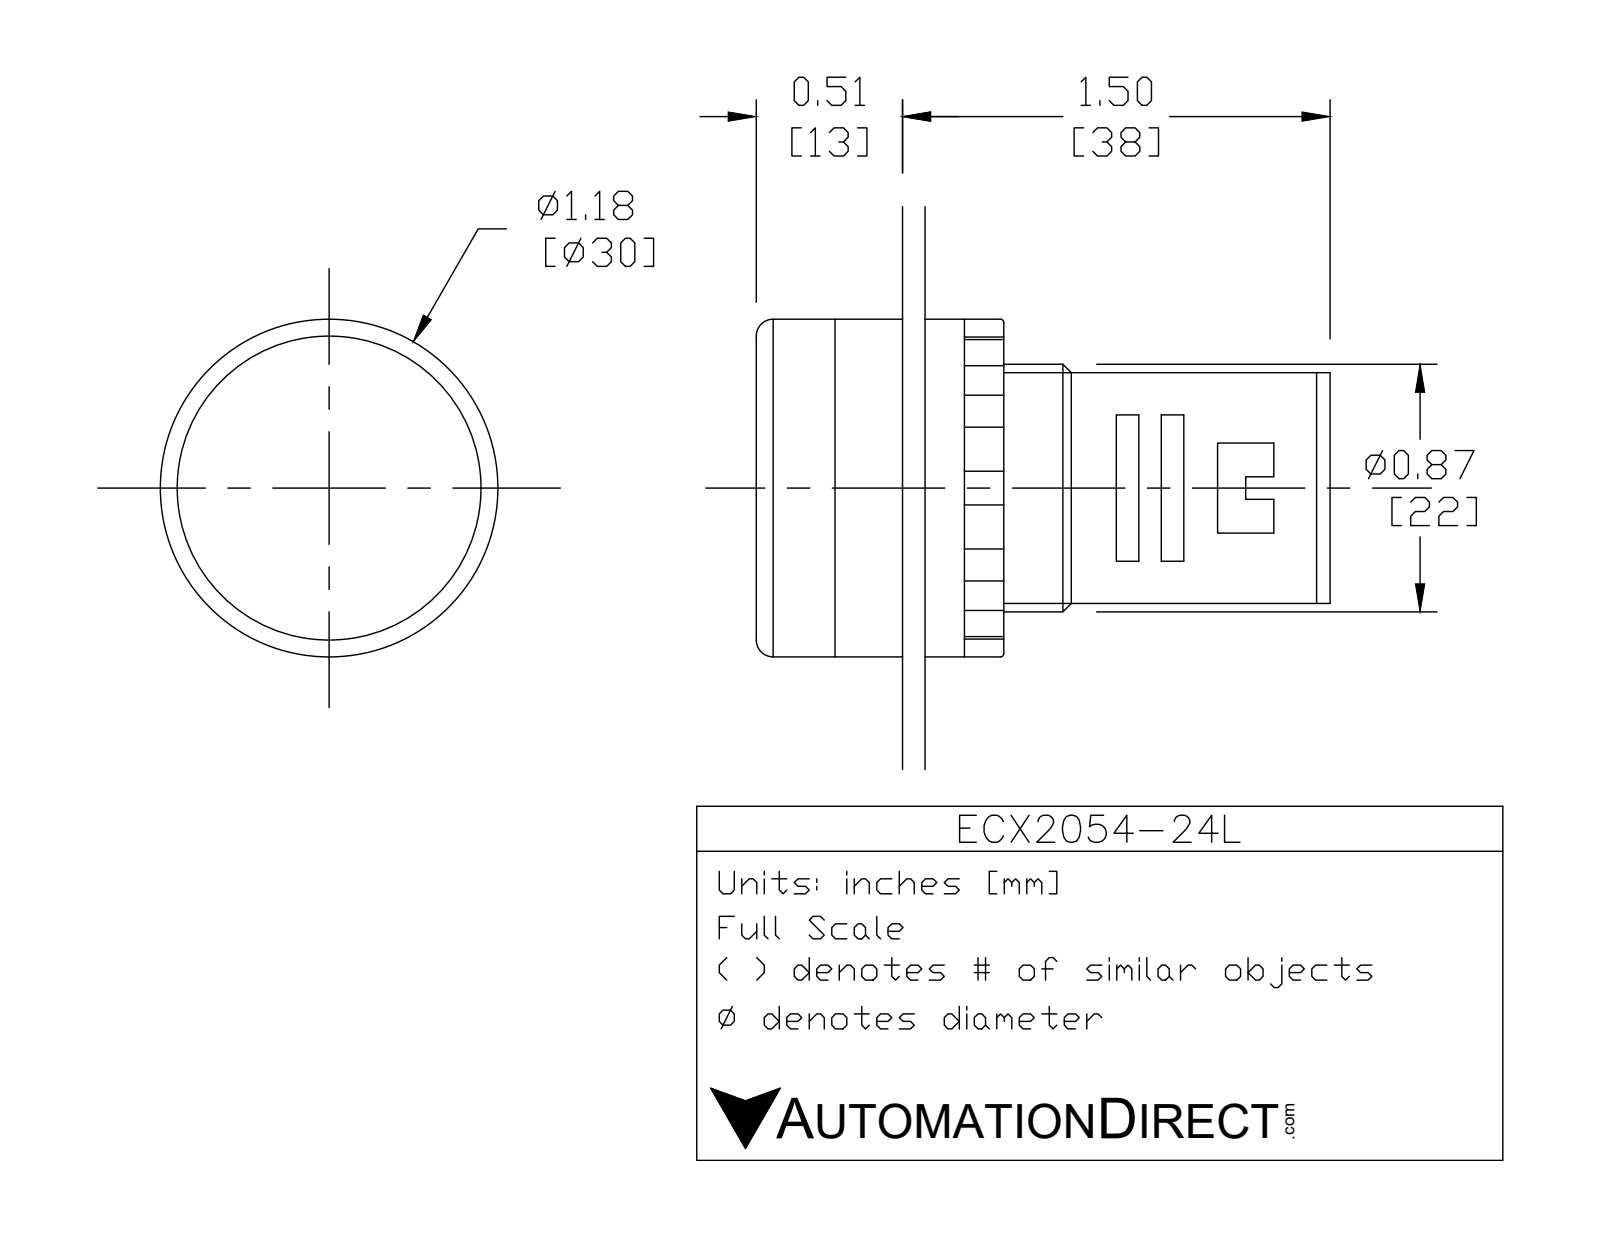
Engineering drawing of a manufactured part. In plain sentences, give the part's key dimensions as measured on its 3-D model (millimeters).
The part is named "ECX2054-24L". Its 3-D file was written by "SolidWorks 2017 (AUTOMOTIVE_DESIGN)". It is 6 solids with 123 faces: 63 planar, 39 cylindrical and 21 other. Overall it measures 51 by 30 by 30 millimeters. Its volume is 22 483 cubic millimeters and its surface area 9 831 square millimeters. Round holes: 2 of diameter 5.5, 1 of diameter 22.5. Round bosses or shafts: 2 of diameter 4, 1 of diameter 30, 1 of diameter 29, 1 of diameter 26.5, 1 of diameter 22, 1 of diameter 20. Partial cylindrical surfaces (rounded edges, fillets, slot ends): 12 of radius 1. The main face-to-face distances are 6, 19, 13, 7, 2, 25, 4, 12, 17, 15. The hole center spacings are 4.62, 9.24.
